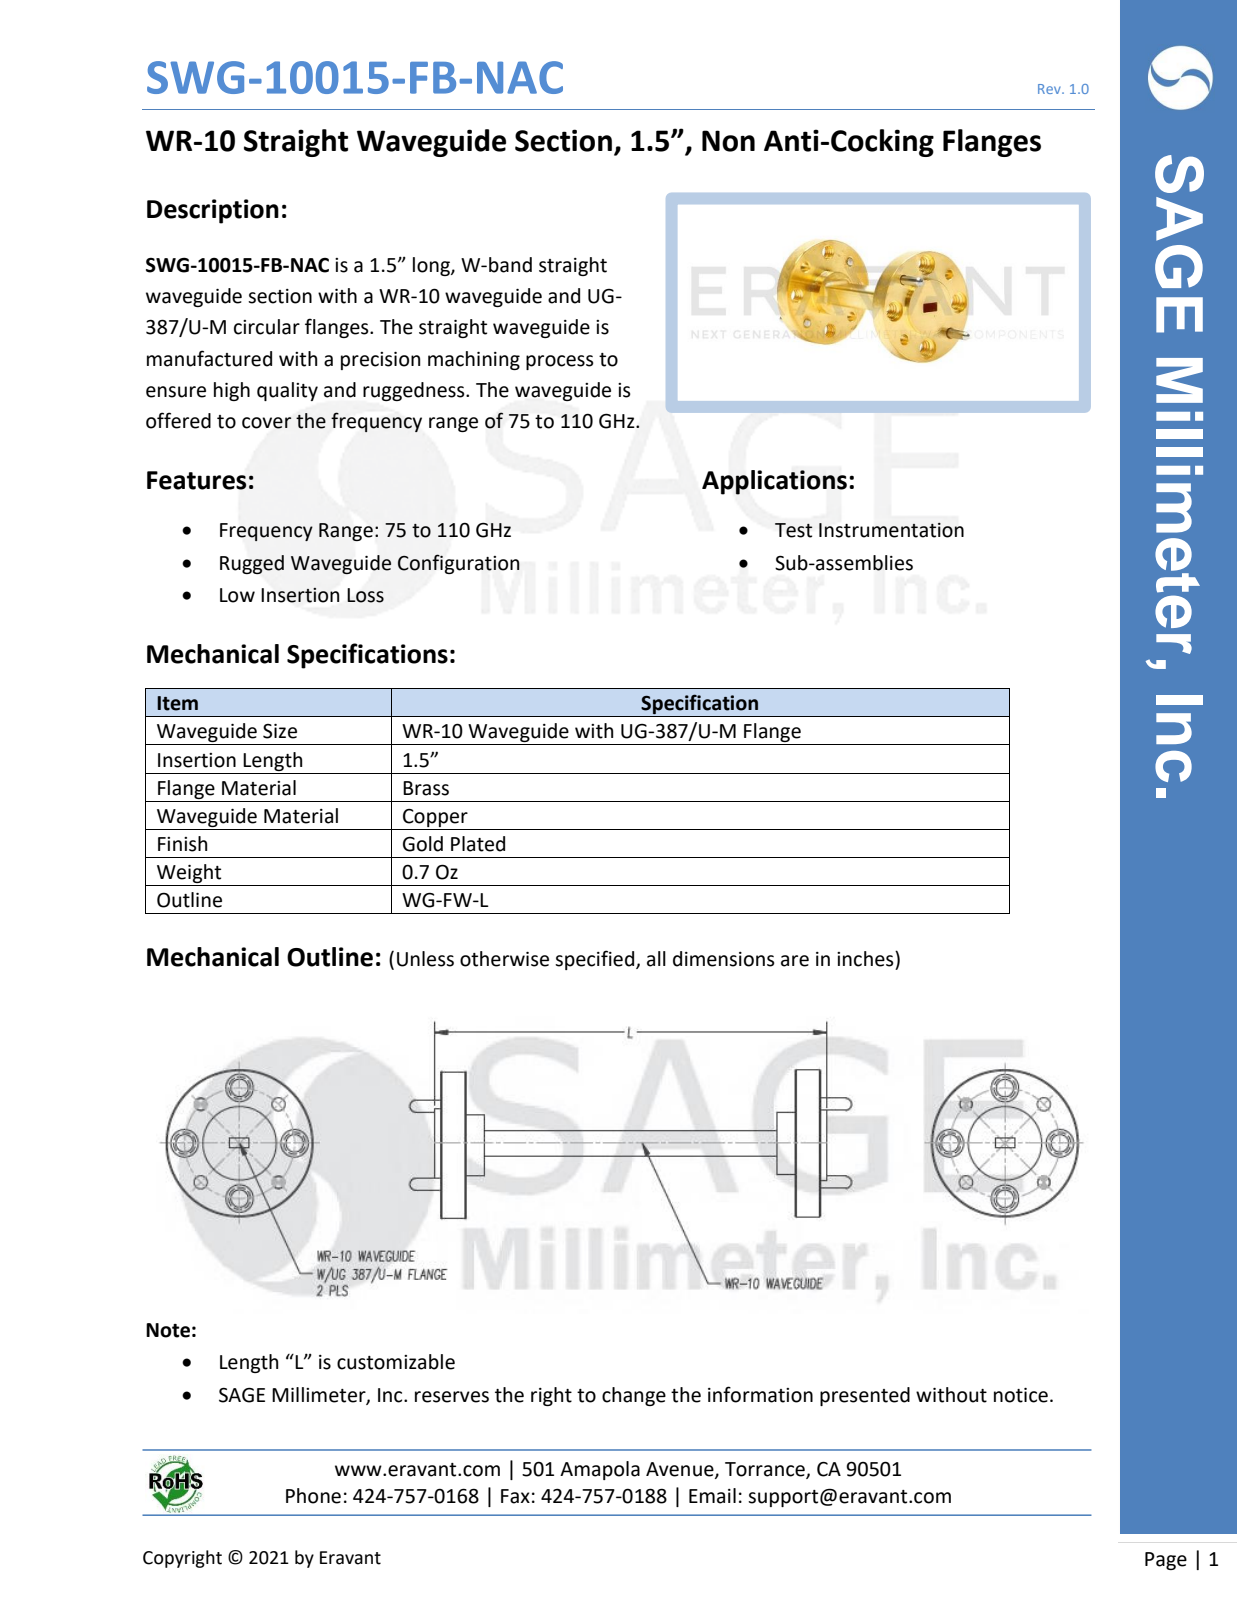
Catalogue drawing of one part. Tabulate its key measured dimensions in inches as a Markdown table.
| quantity | value |
| --- | --- |
| part name | SWG-10015-FB |
| STEP written by | SolidWorks 2020 (CONFIG_CONTROL_DESIGN) |
| units | inches |
| bodies | 5 solids, 146 faces (38 planar, 68 cylindrical, 40 other) |
| overall size | 1.82 × 0.75 × 0.75 |
| volume | 0.155 in³ |
| surface area | 3.812 in² |
| round holes (diameter × count) | 0.061 × 4, 0.067 × 4, 0.089 × 4, 0.14 × 4 |
| round bosses / shafts (diameter × count) | 0.063 × 4, 0.75 × 1, 0.375 × 1, 0.36 × 1 |
| main face-to-face distances | 0.13, 1.31, 1.18, 1.44, 0.16, 0.03, 1.34, 1.47, 0.09, 0.25 |
| hole center spacings | 0.215, 0.398, 0.519, 0.562 |
